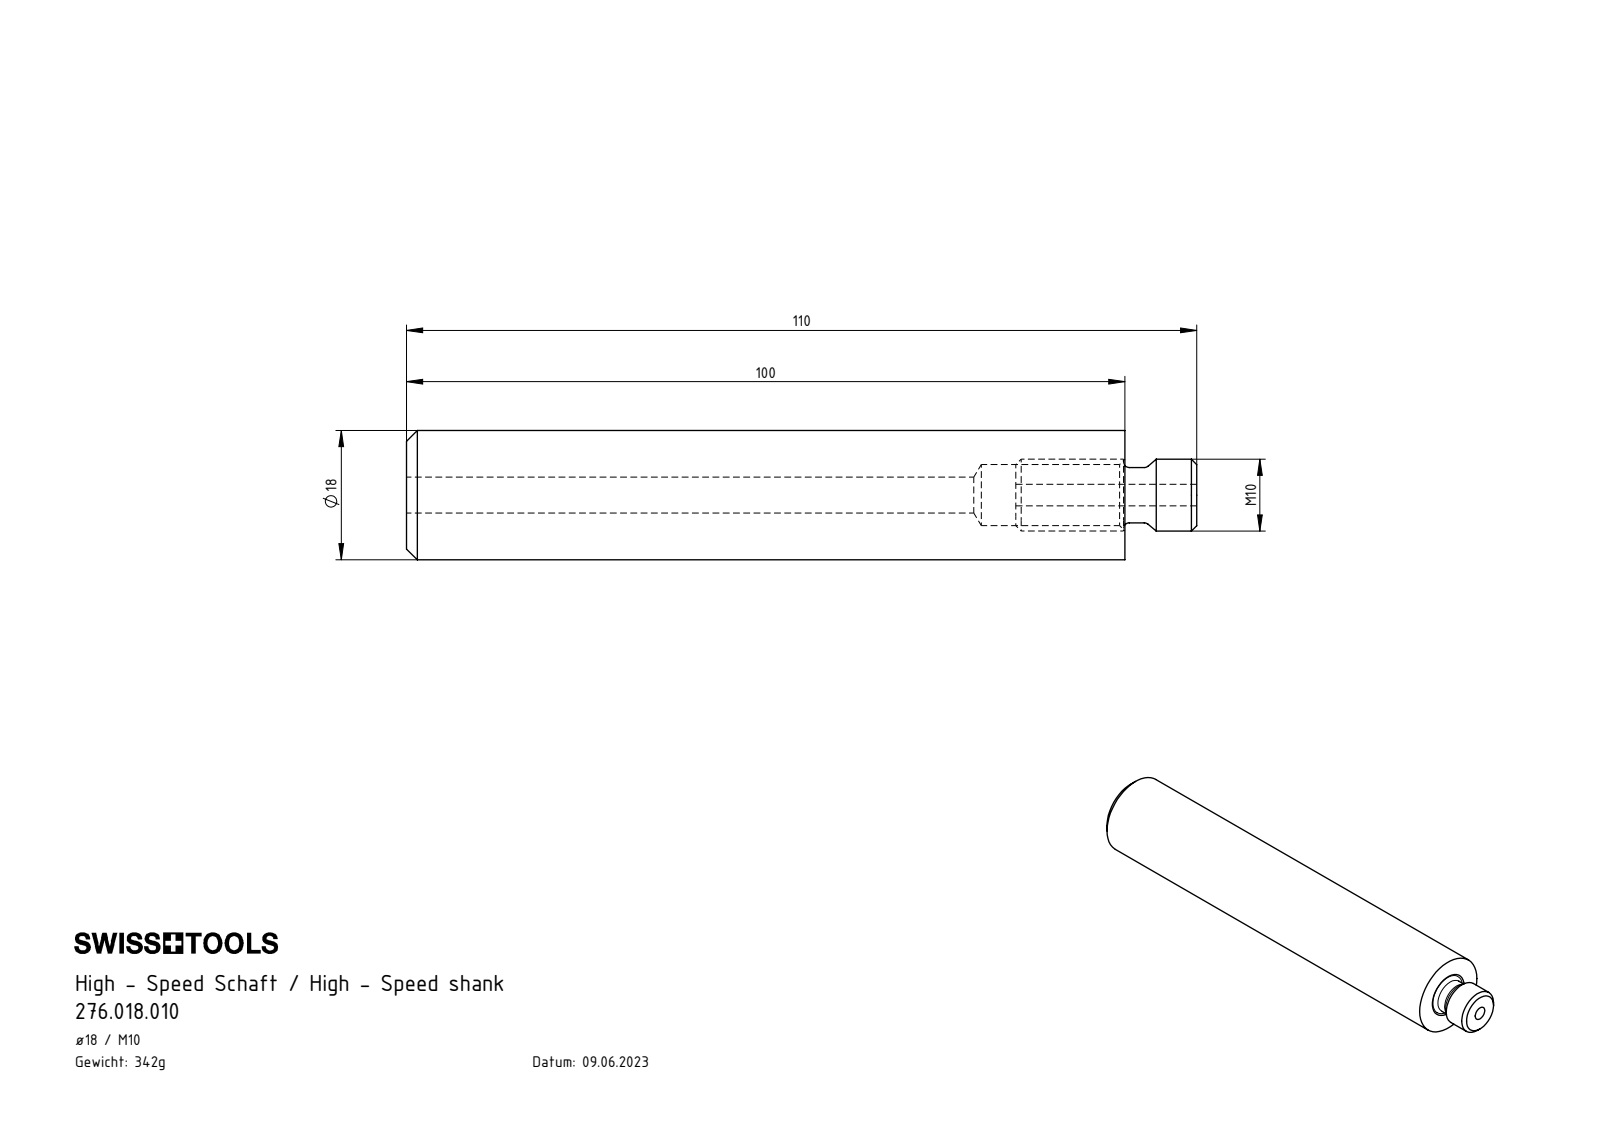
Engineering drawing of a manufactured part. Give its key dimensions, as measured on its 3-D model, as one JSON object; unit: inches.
{"part_name": "276.018.010; HM1-U18.001.100_A; HM1-BG1.010.025_A", "step_written_by": "SolidWorks 2022 (CONFIG_CONTROL_DESIGN)", "units": "inches", "bodies": {"solids": 2, "faces": 35, "planar": 5, "cylindrical": 14, "other": 16}, "overall_size": [4.331, 0.709, 0.709], "volume_in3": 1.484, "surface_area_in2": 13.94, "round_holes": [[0.118, 1], [0.197, 1], [0.335, 1]], "round_bosses_or_shafts": [[0.709, 1], [0.394, 1], [0.303, 1]], "face_to_face_distances": [3.937, 4.331, 0.394, 3.339, 0.598, 0.992, 3.929, 0.591, 0.402]}
